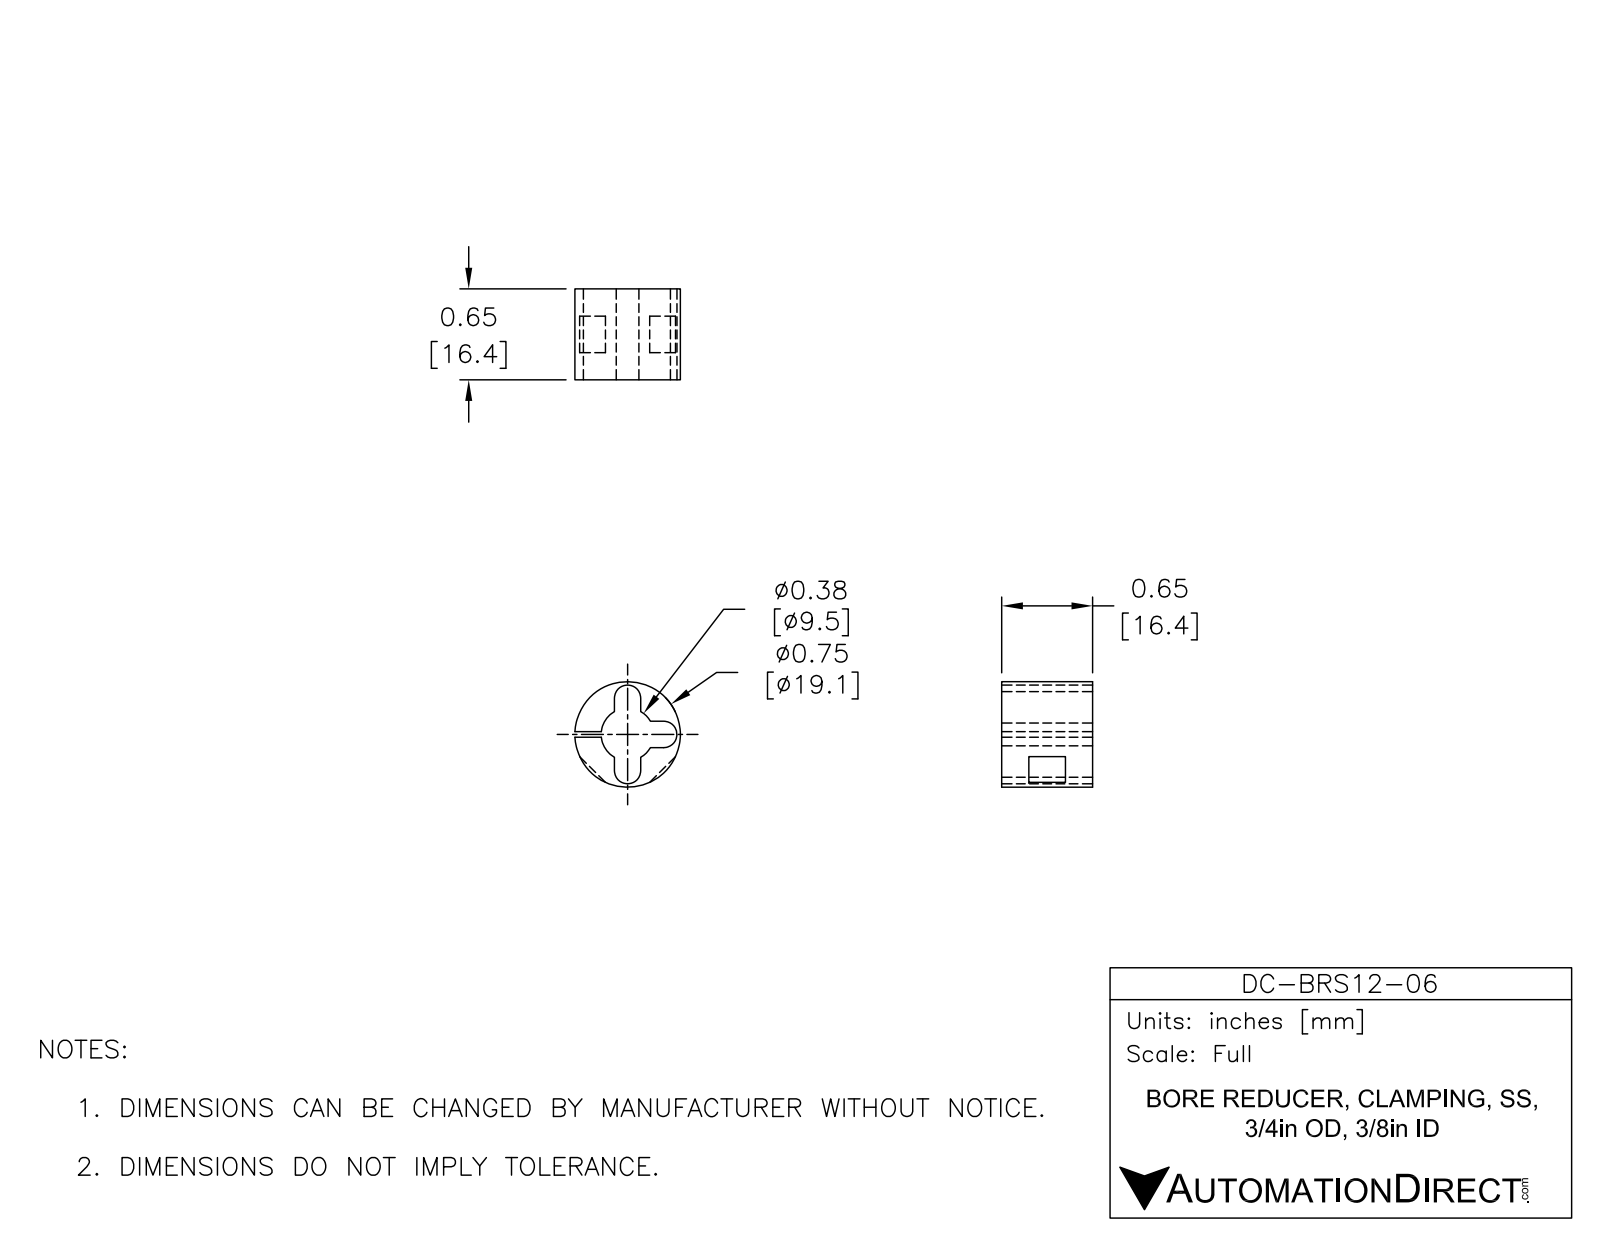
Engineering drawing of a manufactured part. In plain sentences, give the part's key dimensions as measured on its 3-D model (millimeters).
The part is named "DC-BRS12-06". Its 3-D file was written by "SolidWorks 2015 (AUTOMOTIVE_DESIGN)". It is 1 solid with 27 faces: 16 planar, 11 cylindrical and 0 other. Overall it measures 19.05 by 19.04 by 16.41 millimeters. Its volume is 2 495 cubic millimeters and its surface area 2 272 square millimeters. Round bosses or shafts: 1 of diameter 19.05. Partial cylindrical surfaces (rounded edges, fillets, slot ends): 3 of radius 2.38, 1 of radius 4.76, 1 of radius 4.76. The main face-to-face distances are 16.4, 4.76, 1.87, 2.89, 1.02, 4.9, 11.5, 6.6.
